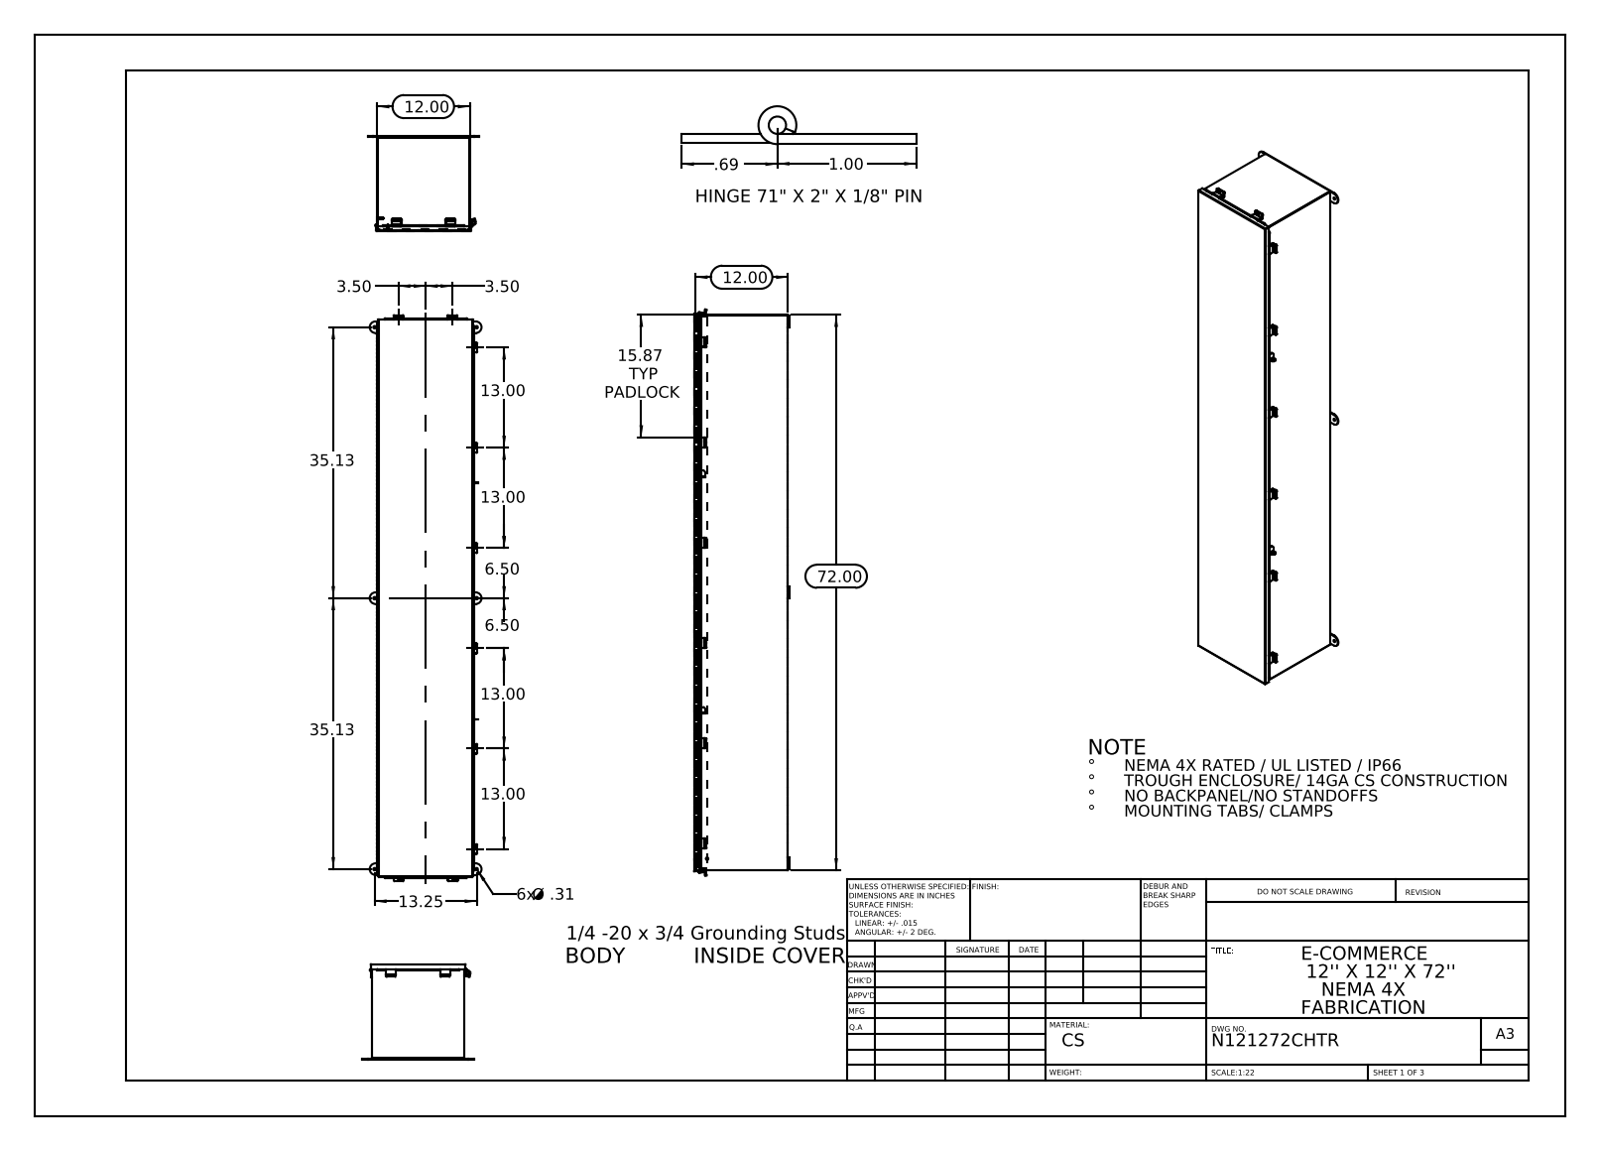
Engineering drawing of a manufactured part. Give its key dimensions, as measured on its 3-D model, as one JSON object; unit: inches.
{"part_name": "N121272SSCHTR Hinge Cover Side JIC; N121272SSCHTR JIC Clamp Bracket; N121272SSCHTR JIC Cover Clamp; N121272SSCHTR JIC Top (+8 more)", "step_written_by": "SolidWorks 2013 (CONFIG_CONTROL_DESIGN)", "units": "inches", "bodies": {"solids": 33, "faces": 2035, "planar": 1218, "cylindrical": 797, "other": 20}, "overall_size": [73.407, 14.5, 12.337], "volume_in3": 313.2, "surface_area_in2": 8388, "round_holes": [[0.25, 10], [0.313, 6], [0.125, 1], [0.125, 1], [0.375, 1]], "round_bosses_or_shafts": [[0.315, 2], [0.236, 2], [0.273, 1], [0.25, 1]], "partial_cylinders_radius": [[0.125, 38], [0.133, 20], [0.009, 12], [0.013, 10], [0.088, 10], [0.083, 6], [0.1, 6], [0.75, 6]], "face_to_face_distances": [0.075, 11.925, 12.128, 12, 11.85, 12.203, 12.053, 71.925, 0.149, 12.074], "hole_center_spacings": [13, 26, 35.125, 37.541, 13.25, 39, 7, 52]}
